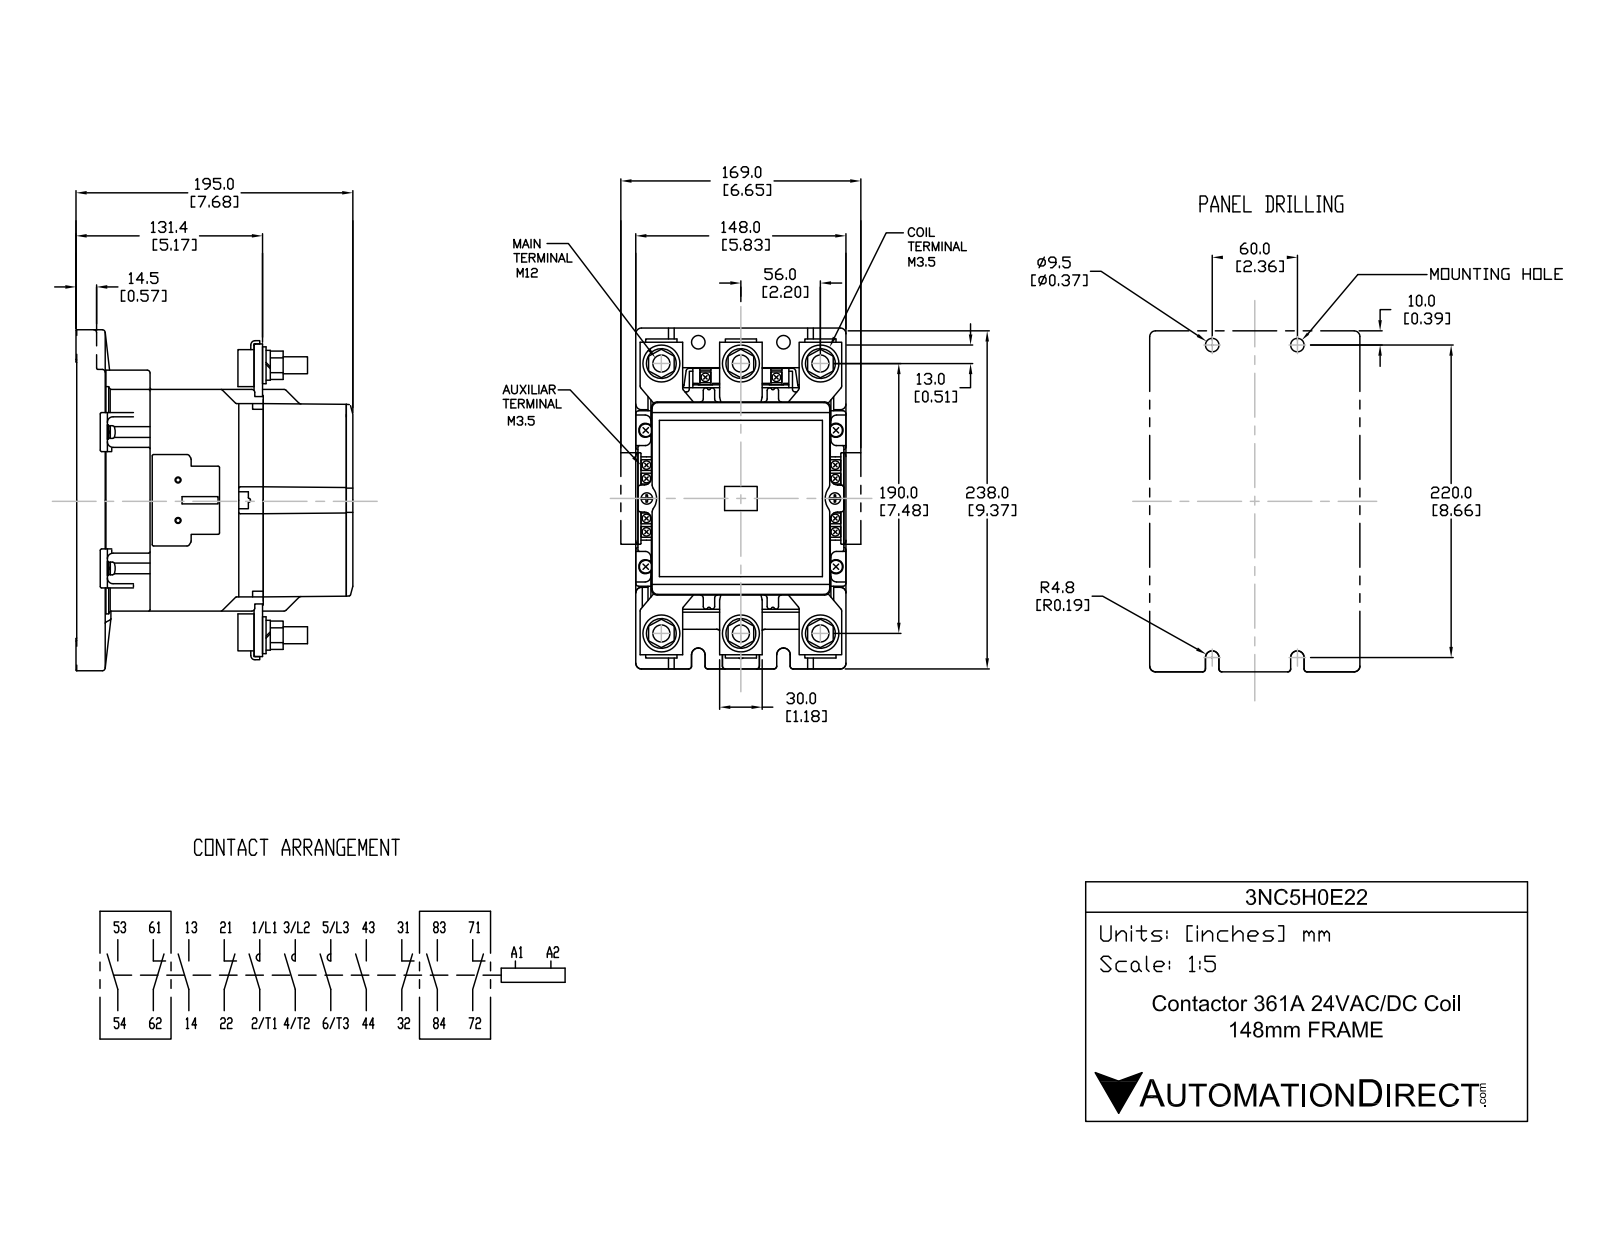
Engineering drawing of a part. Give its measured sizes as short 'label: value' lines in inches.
name: 3NC5H0E22
written by: SolidWorks 2018 (AUTOMOTIVE_DESIGN)
unit: in
bodies: 20 solids, 375 faces (261 planar, 114 cylindrical, 0 other)
size: 9.449 × 7.677 × 5.866
volume: 256.1 in³; area: 431.1 in²
holes: 6× ⌀0.472, 2× ⌀0.315, 2× ⌀0.394
rounds: 26× R0.079, 16× R0.157, 12× R0.039, 8× R0.031, 6× R0.197, 2× R0.02
face distances: 4.528, 0.433, 4.961, 0.394, 5.748, 5.394, 3.15, 7.677, 0.827, 3.701
hole spacings: 2.244, 3.765, 4.6, 6.181, 7.81, 7.48, 1.213, 1.324
